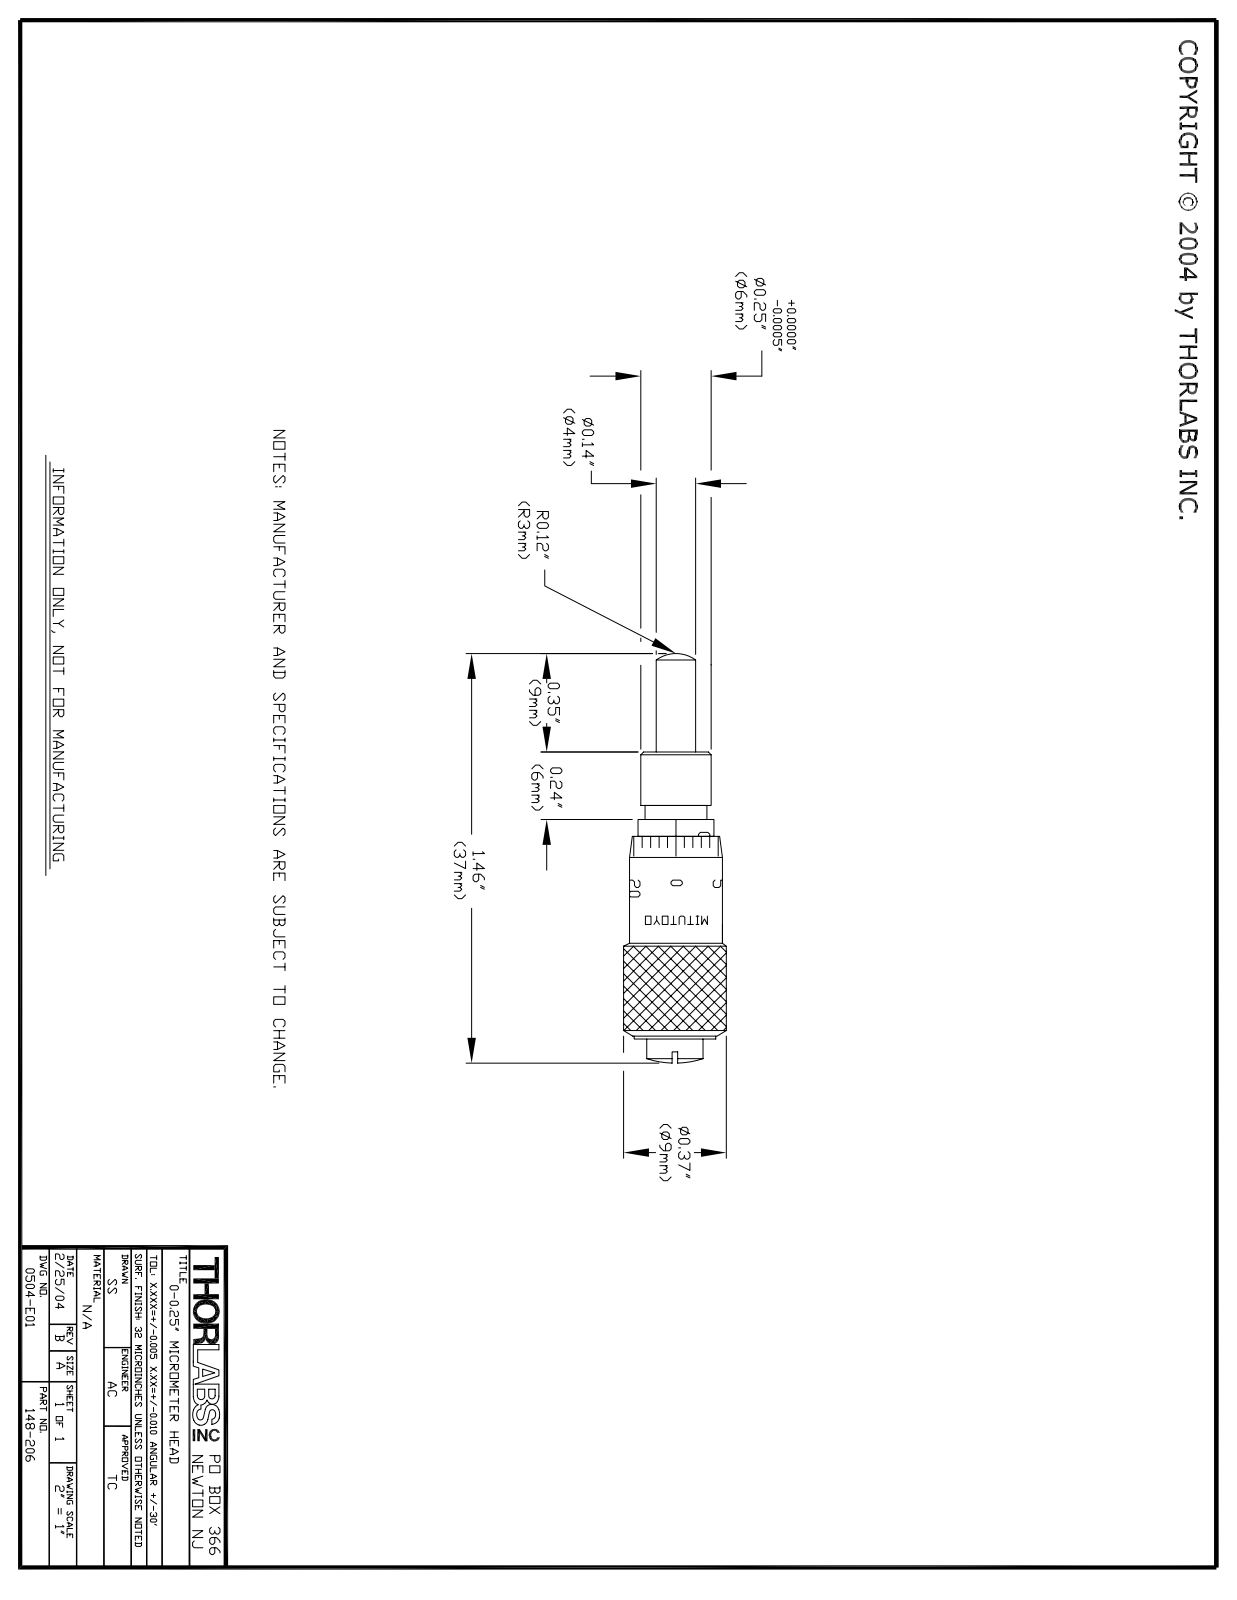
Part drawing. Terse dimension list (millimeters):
name: 0504-E0W
written by: SolidWorks 2007 (AUTOMOTIVE_DESIGN)
unit: mm
bodies: 0 solids, 39 faces (9 planar, 16 cylindrical, 14 other)
size: 37 × 9.3 × 9.3
bosses: 1× ⌀9.3, 1× ⌀8.6, 1× ⌀7.4, 1× ⌀7, 1× ⌀6.5, 1× ⌀5.8, 1× ⌀5.1, 1× ⌀3.7
face distances: 25.9, 6.1, 19.8, 7.6, 1.5, 18.3, 4.8, 1.3, 2.8, 21.1
